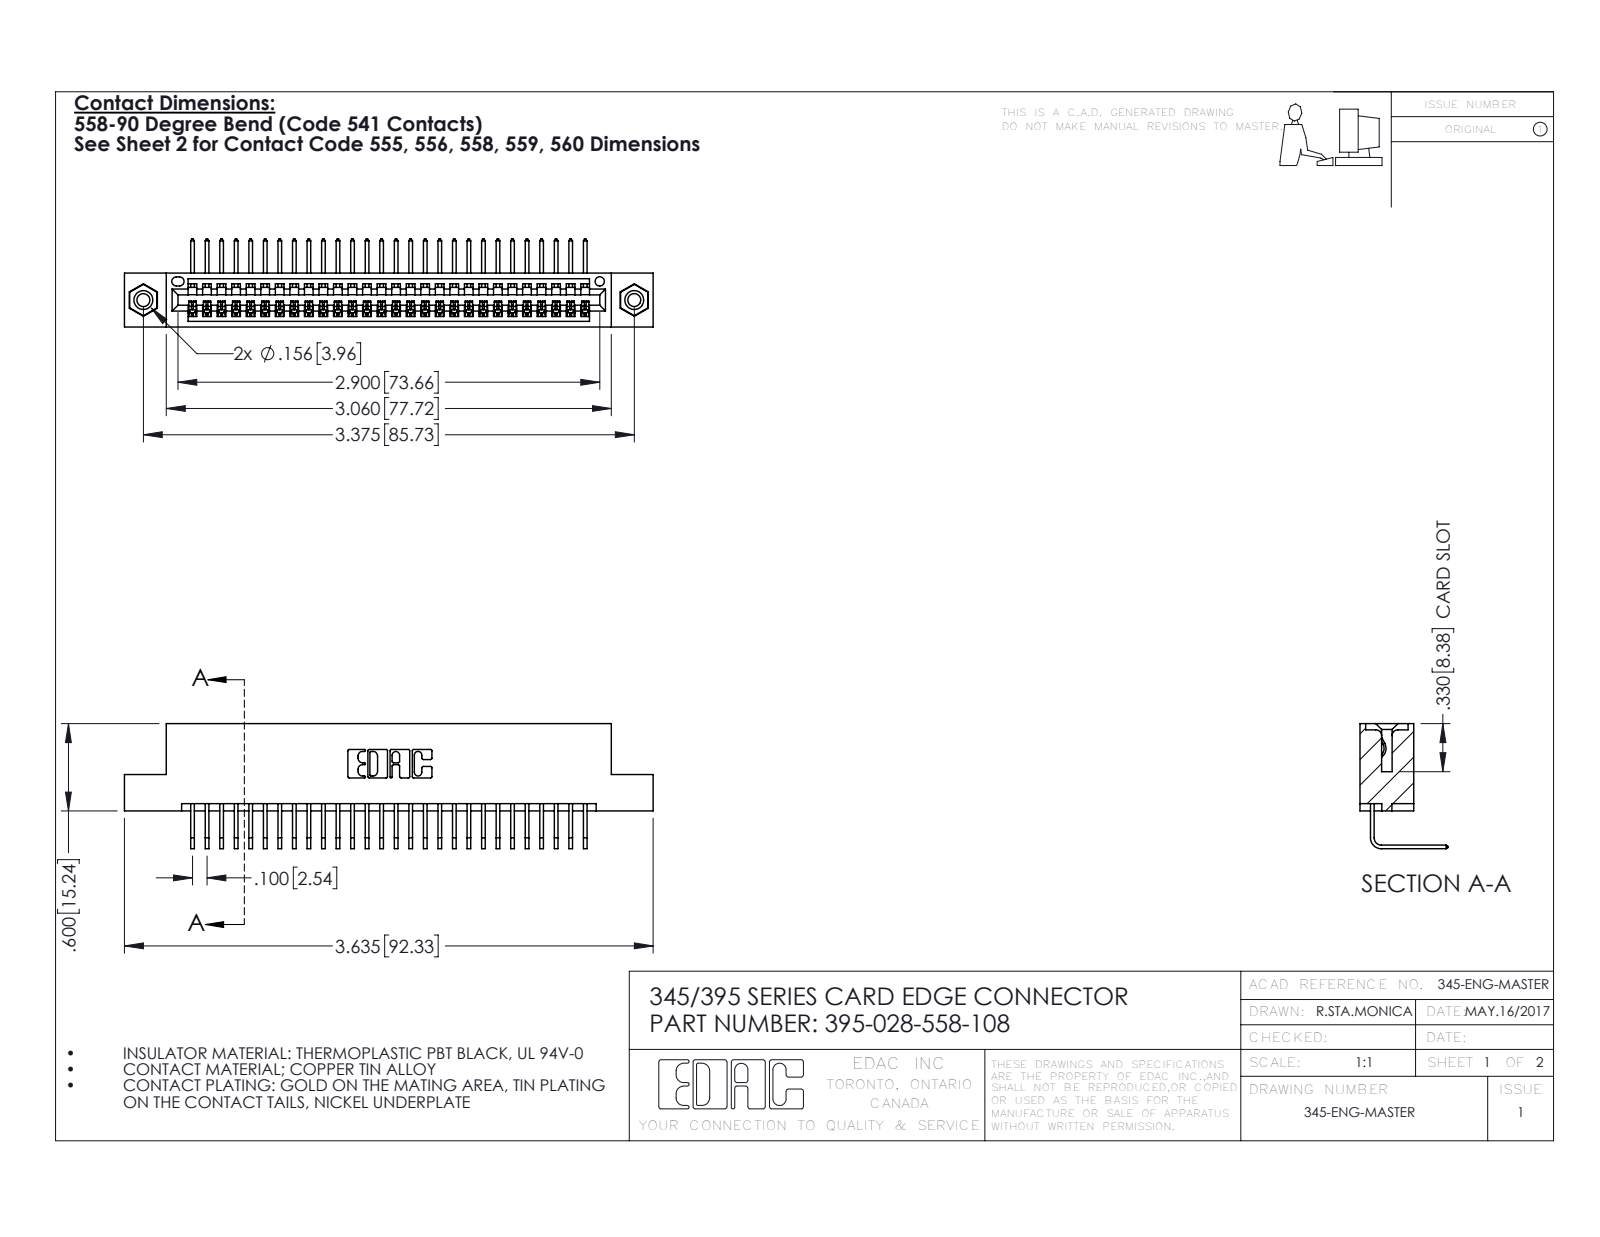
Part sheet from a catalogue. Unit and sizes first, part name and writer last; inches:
Units: inches
Overall size (bounding box): 3.635 × 0.859 × 0.605
Round holes (diameter × count): ⌀0.089 ×2, ⌀0.125 ×2, ⌀0.156 ×2, ⌀0.064 ×1
Round bosses / shafts (diameter × count): ⌀0.155 ×2
Partial cylindrical surfaces — rounded edges, fillets, slot ends (radius × count): R0.006 ×56, R0.01 ×22, R0.007 ×6, R0.031 ×6, R0.026 ×3, R0.031 ×2, R0.04 ×2, R0.014 ×1
Main face-to-face distances: 0.072, 0.298, 0.2, 0.37, 0.098, 0.272, 0.025, 0.225, 0.149, 0.072
Hole centre spacings: 0.27, 3.14, 3.375
Volume: 0.533 in³ · Surface area: 18.59 in²
Bodies: 31 solids, 1866 faces (1288 planar, 562 cylindrical, 16 other)
Part name (STEP PRODUCT): 345-292-001_558 Tail - 2; 395-028-558-108; 345 Part_Flush Mounting Lugs - 0.156 Dia-TI; 345-250-001_345-250-003-102
STEP written by: SolidWorks 2016 (CONFIG_CONTROL_DESIGN)
